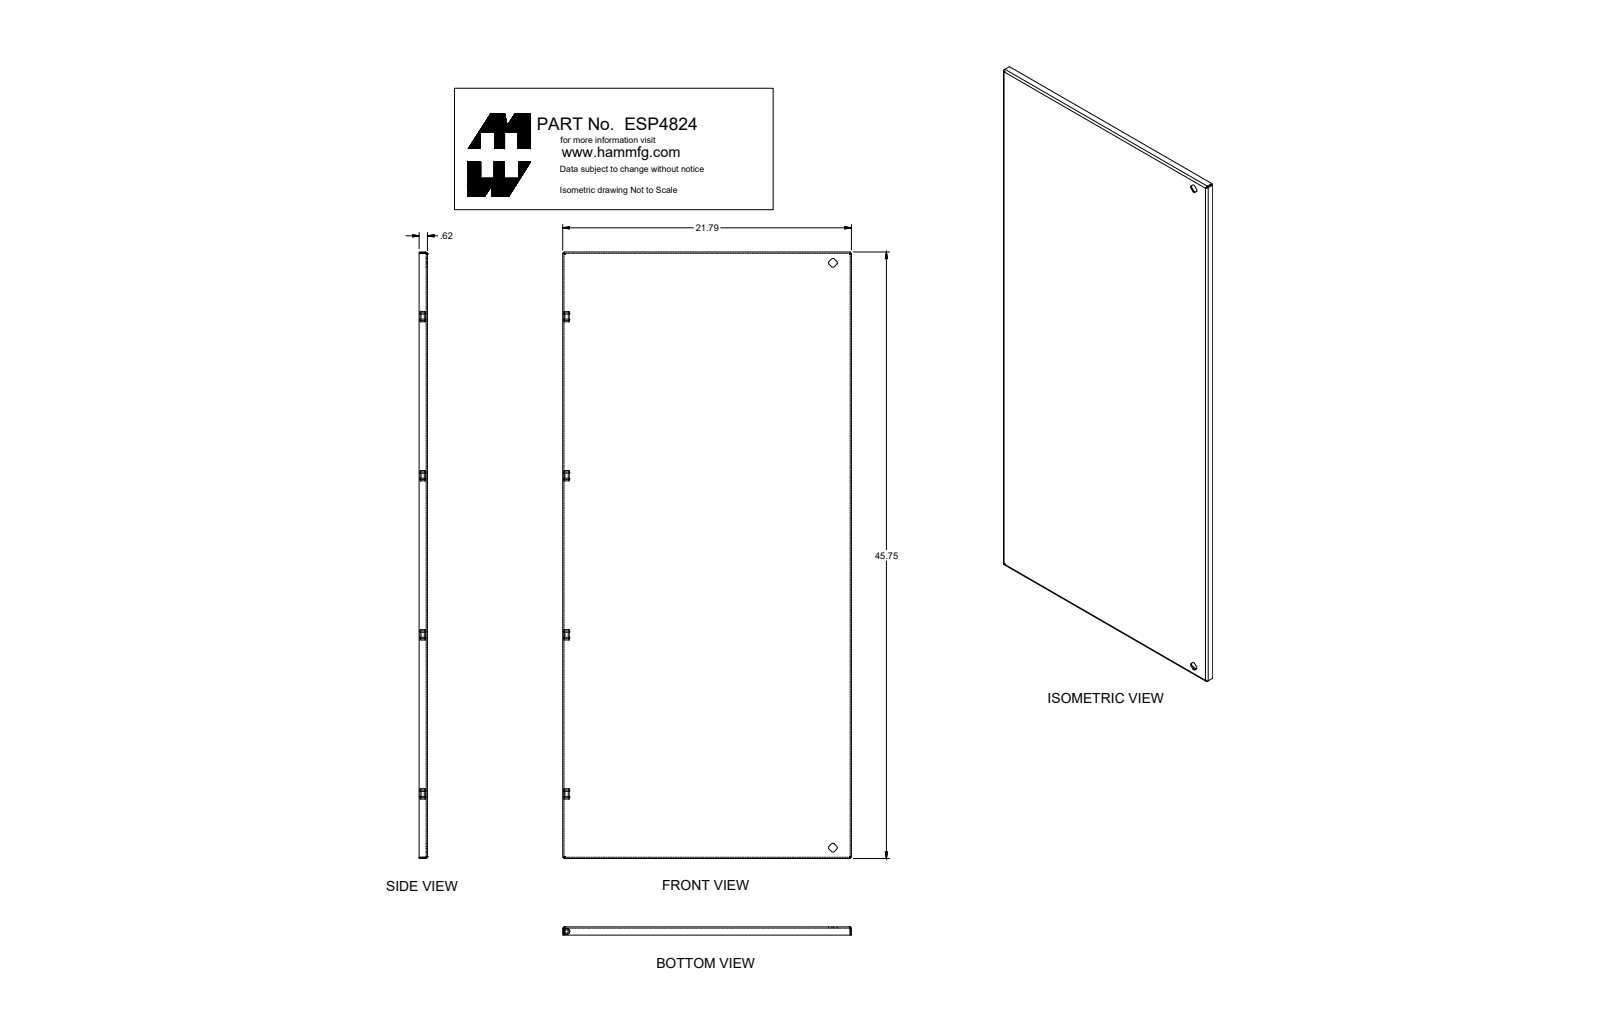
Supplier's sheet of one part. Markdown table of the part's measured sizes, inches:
| quantity | value |
| --- | --- |
| part name | ESP4824 |
| STEP written by | SolidWorks 2018 (AUTOMOTIVE_DESIGN) |
| units | inches |
| bodies | 28 solids, 1012 faces (523 planar, 361 cylindrical, 128 other) |
| overall size | 45.75 × 23.856 × 6.757 |
| volume | 127.7 in³ |
| surface area | 2 979 in² |
| round holes (diameter × count) | 0.281 × 6, 0.172 × 3, 0.242 × 3, 0.516 × 2, 0.24 × 1, 0.797 × 1 |
| round bosses / shafts (diameter × count) | 0.356 × 3, 0.292 × 3, 0.226 × 3, 0.788 × 2, 0.535 × 2, 0.496 × 2, 0.435 × 2, 0.455 × 1 |
| partial cylindrical surfaces (radius × count) | 0.048 × 40, 0.01 × 36, 0.006 × 8, 0.063 × 8, 0.036 × 6, 0.108 × 6, 0.156 × 6, 0.06 × 4 |
| main face-to-face distances | 0.095, 0.072, 22.158, 0.748, 0.843, 0.82, 0.915, 22.23, 22.086, 0.775 |
| hole center spacings | 22, 22.431, 4.375, 44, 44.217, 0.062, 44.098, 44.159 |
